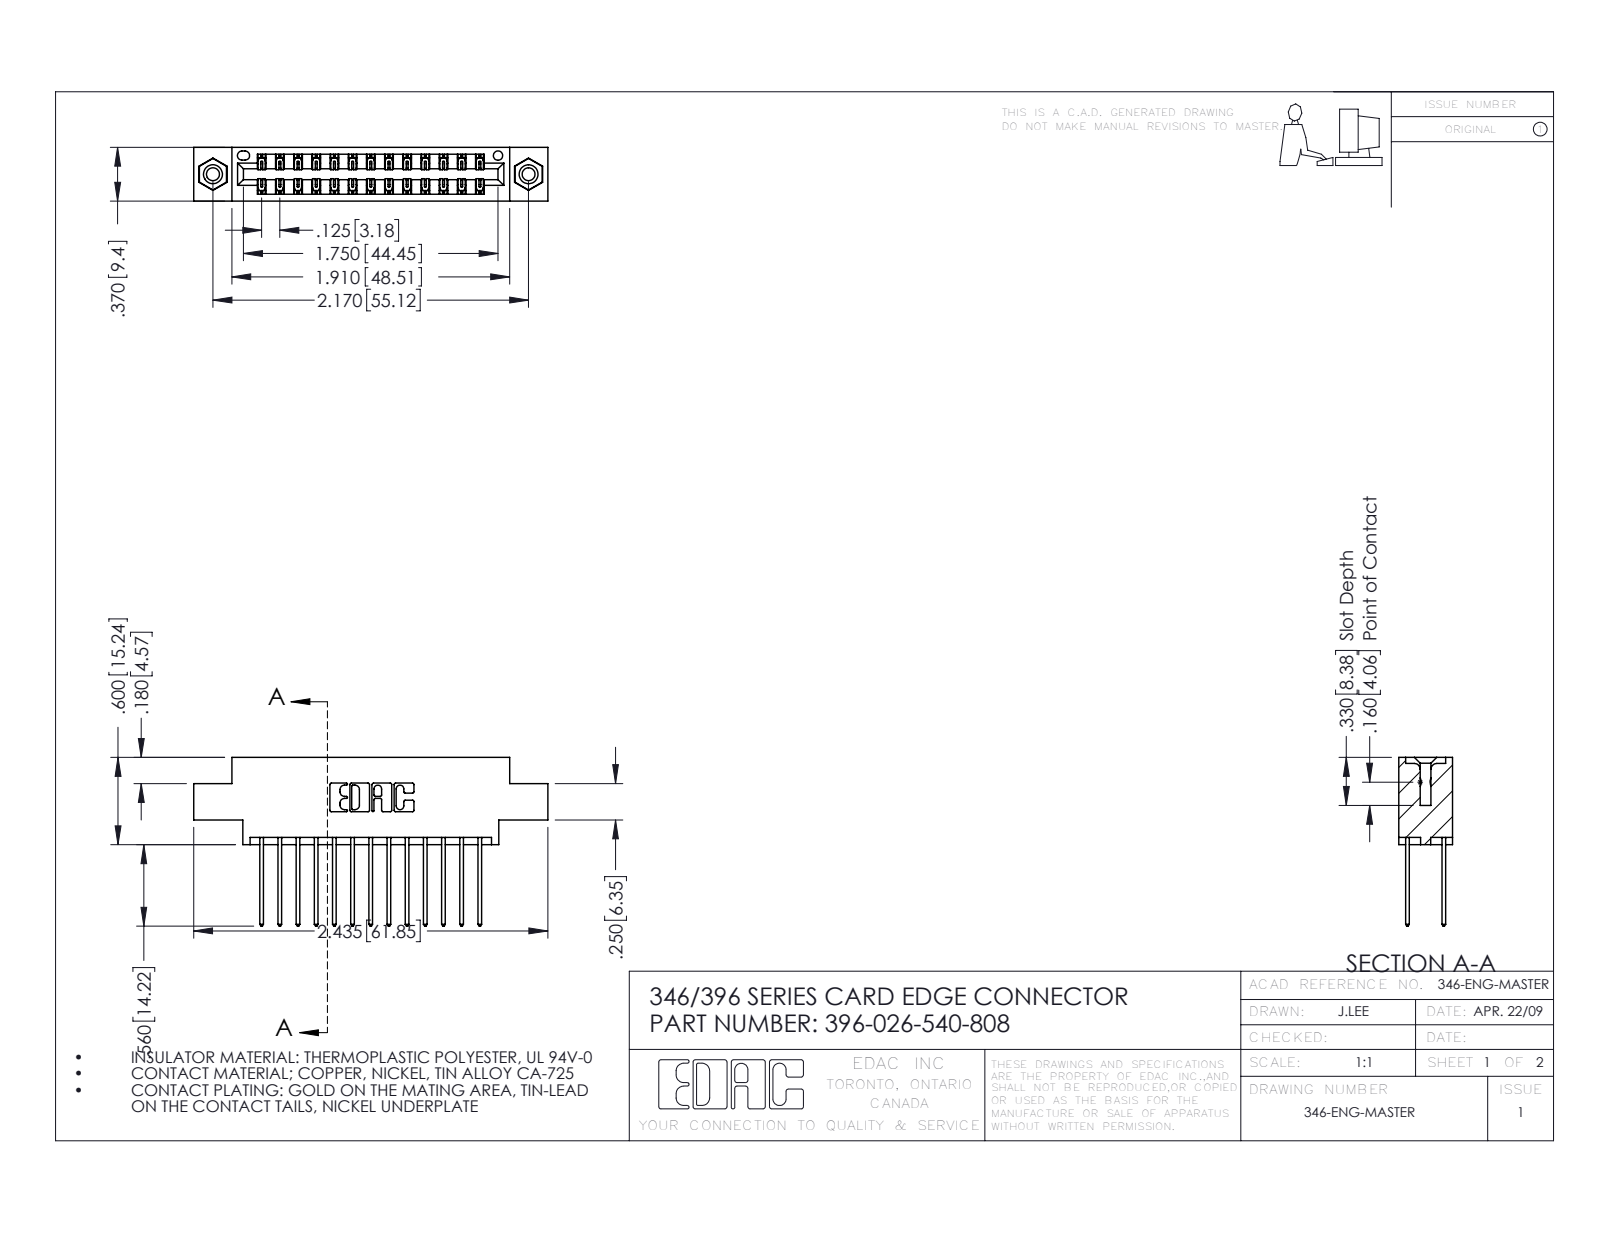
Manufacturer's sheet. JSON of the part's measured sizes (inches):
{"part_name": "345-250-001_345-250-003-102; 396-026-540-808; 346 Part_0.170 Offset - 0.156 Dia-TI; 345-292-001_345-293-140", "step_written_by": "SolidWorks 2016 (CONFIG_CONTROL_DESIGN)", "units": "inches", "bodies": {"solids": 29, "faces": 1538, "planar": 1022, "cylindrical": 500, "other": 16}, "overall_size": [2.435, 1.16, 0.37], "volume_in3": 0.35, "surface_area_in2": 12.56, "round_holes": [[0.089, 2], [0.125, 2], [0.156, 2], [0.064, 1]], "round_bosses_or_shafts": [[0.155, 2]], "partial_cylinders_radius": [[0.006, 39], [0.01, 26], [0.01, 22], [0.007, 6], [0.031, 6], [0.026, 3], [0.014, 2], [0.022, 2]], "face_to_face_distances": [0.048, 0.322, 0.25, 0.37, 0.072, 0.298, 0.025, 0.275, 0.222, 0.148], "hole_center_spacings": [0.246, 1.964, 2.17]}
